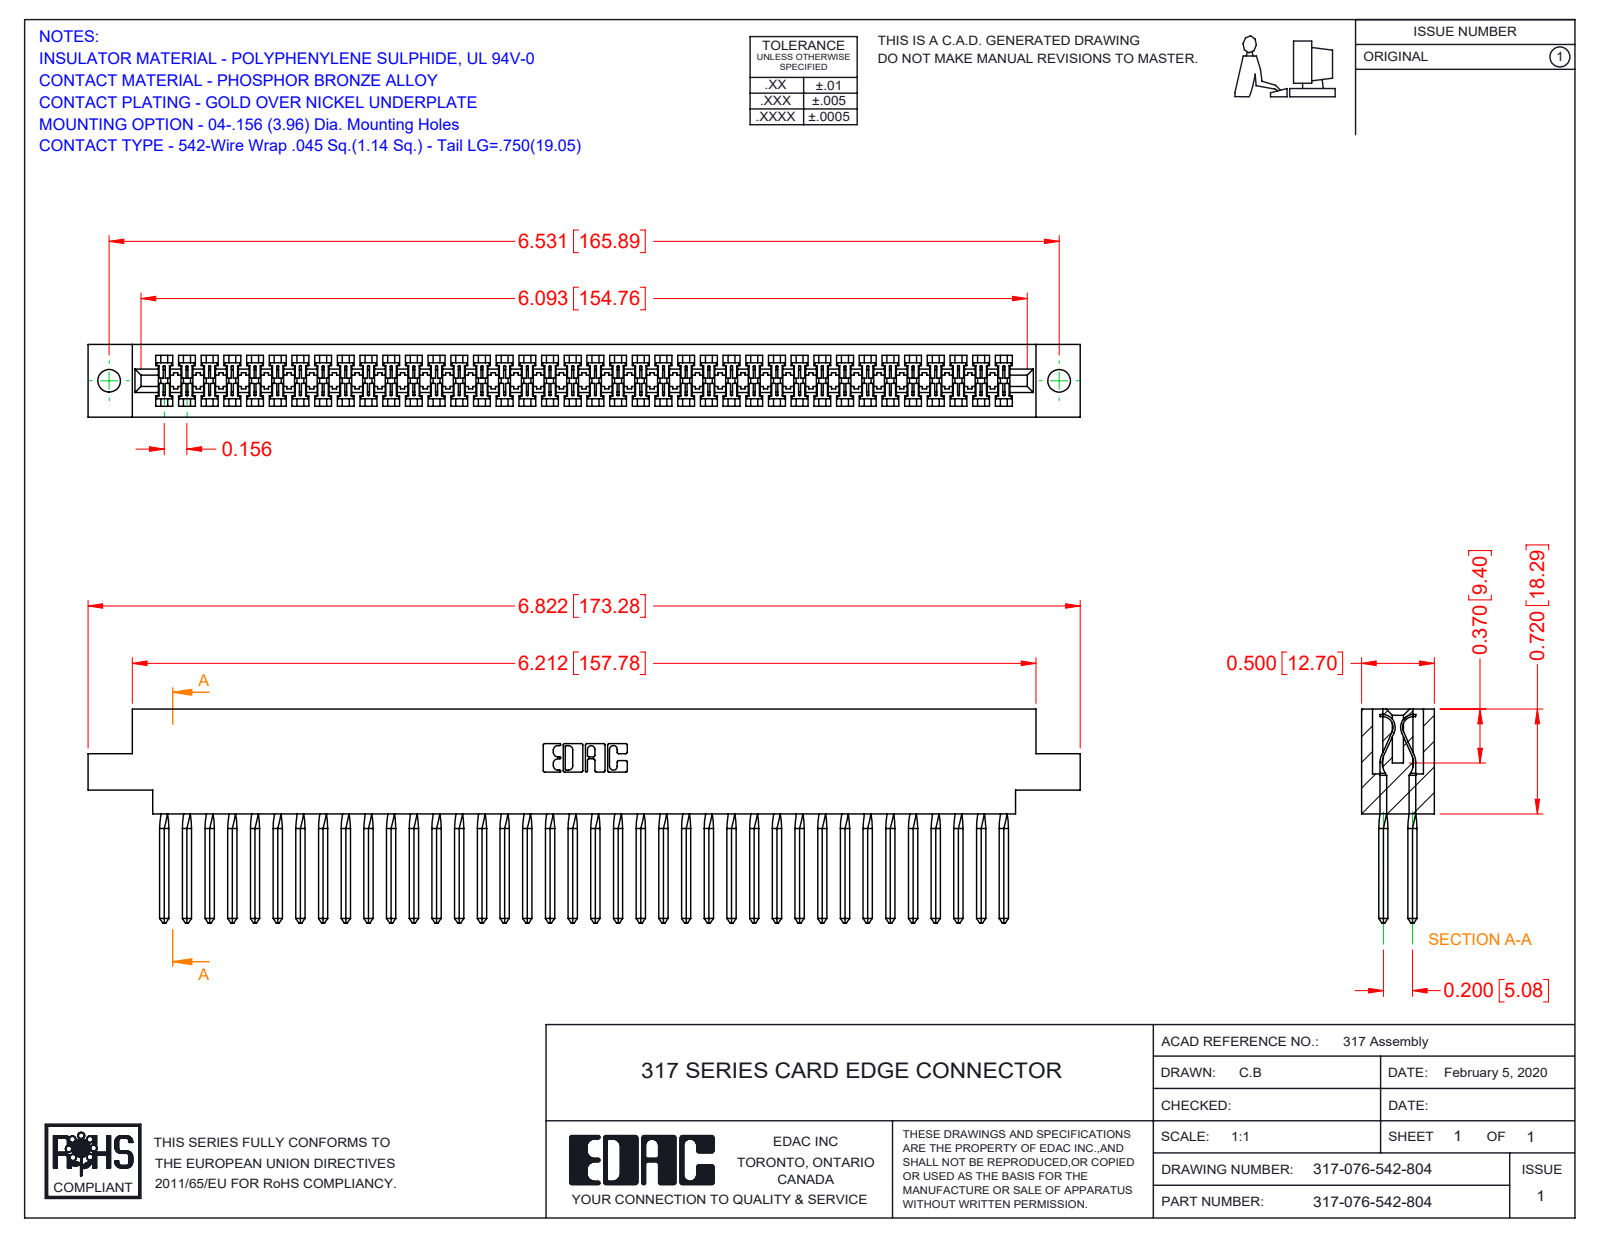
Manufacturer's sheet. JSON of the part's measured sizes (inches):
{"part_name": "317-076-542-804; 317-290-003_542; 317 Part_.156 Dia - TH", "step_written_by": "SolidWorks 2016 (CONFIG_CONTROL_DESIGN)", "units": "inches", "bodies": {"solids": 77, "faces": 4434, "planar": 3554, "cylindrical": 576, "other": 304}, "overall_size": [6.822, 1.47, 0.5], "volume_in3": 1.718, "surface_area_in2": 60.21, "round_holes": [[0.156, 2]], "partial_cylinders_radius": [[0.006, 152], [0.01, 22], [0.007, 6], [0.031, 6], [0.026, 3], [0.074, 2], [0.089, 2], [0.1, 2]], "face_to_face_distances": [0.5, 0.075, 0.425, 0.35, 0.2, 0.046, 0.128, 0.372, 0.052, 0.297], "hole_center_spacings": [6.531]}
